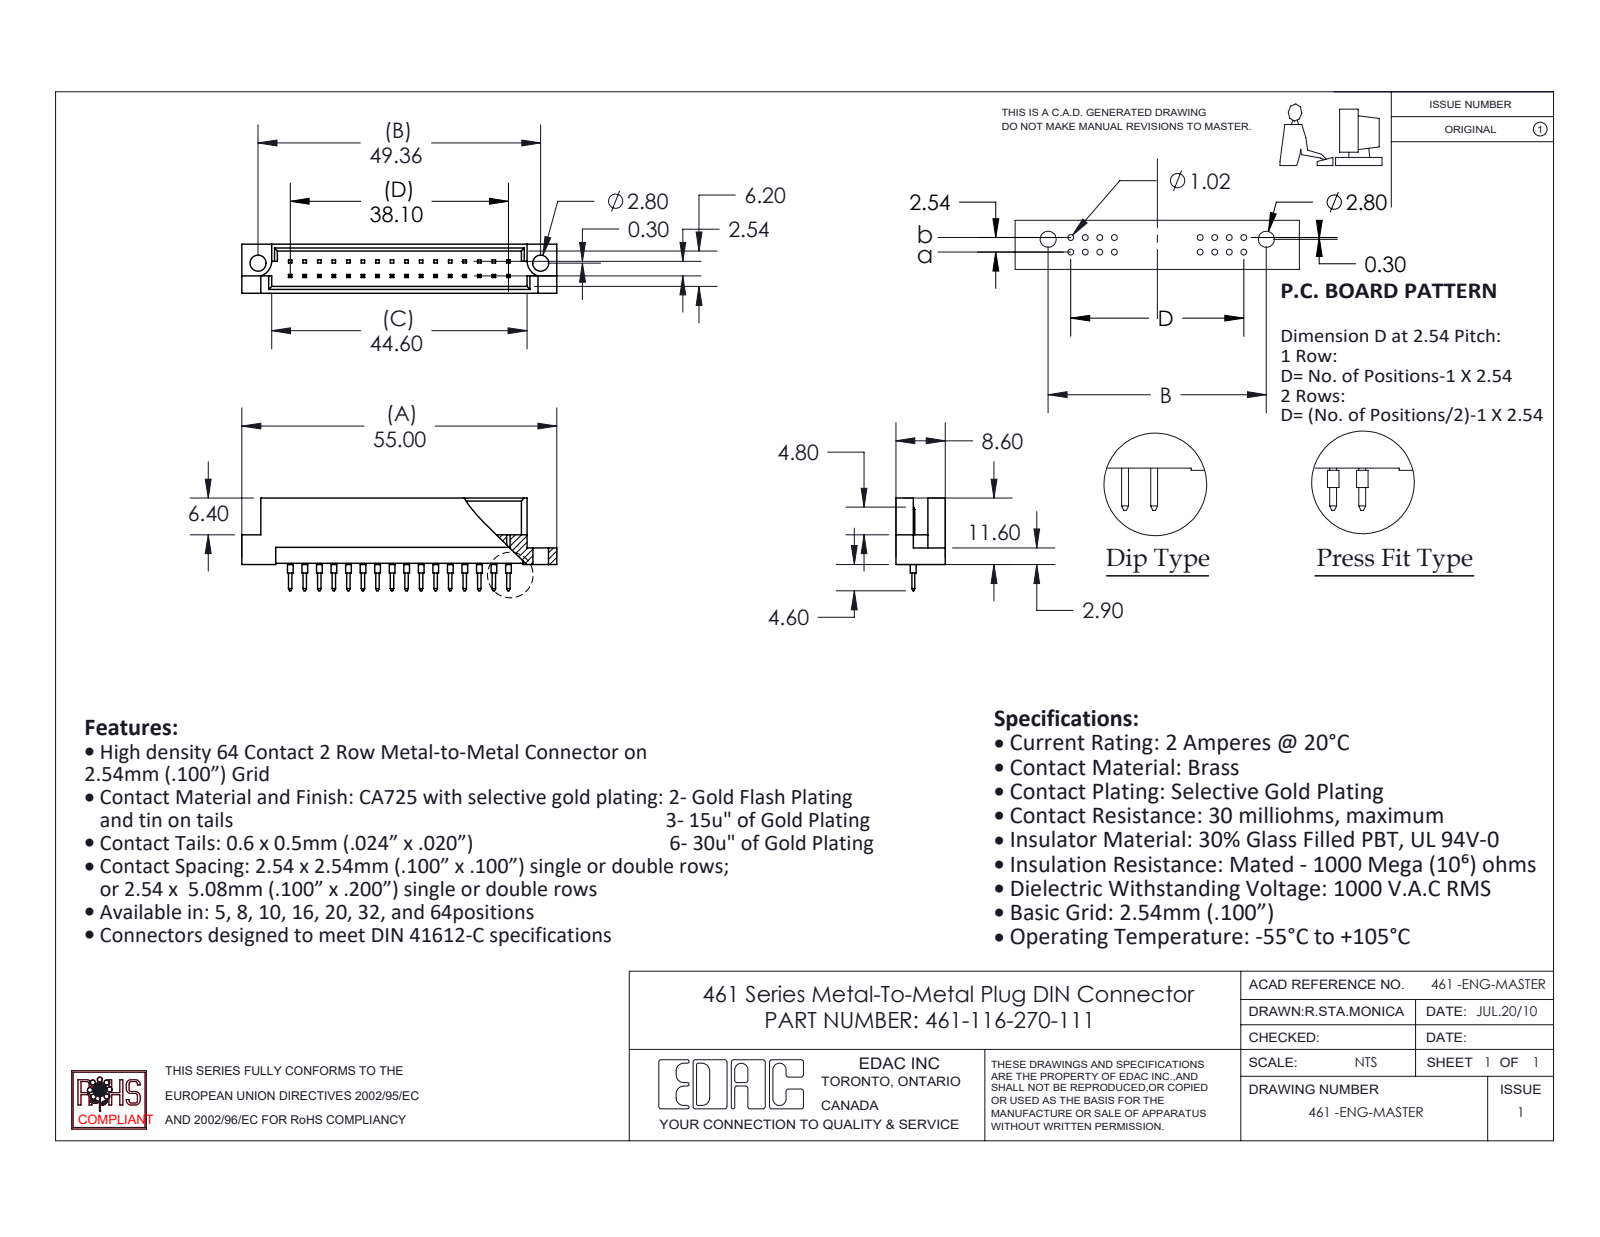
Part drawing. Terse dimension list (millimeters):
name: 461 Part_32; 461-290_70; 461-116-270-111
written by: SolidWorks 2020 (CONFIG_CONTROL_DESIGN)
unit: mm
bodies: 17 solids, 528 faces (490 planar, 38 cylindrical, 0 other)
size: 55 × 16.2 × 8.6
volume: 2 734 mm³; area: 3 794 mm²
holes: 2× ⌀2.8
bosses: 16× ⌀1
rounds: 2× R2.8
face distances: 1.2, 7.4, 8.6, 6.2, 5, 2.54, 1.58, 2.78, 5.82, 4.62
hole spacings: 49.36
